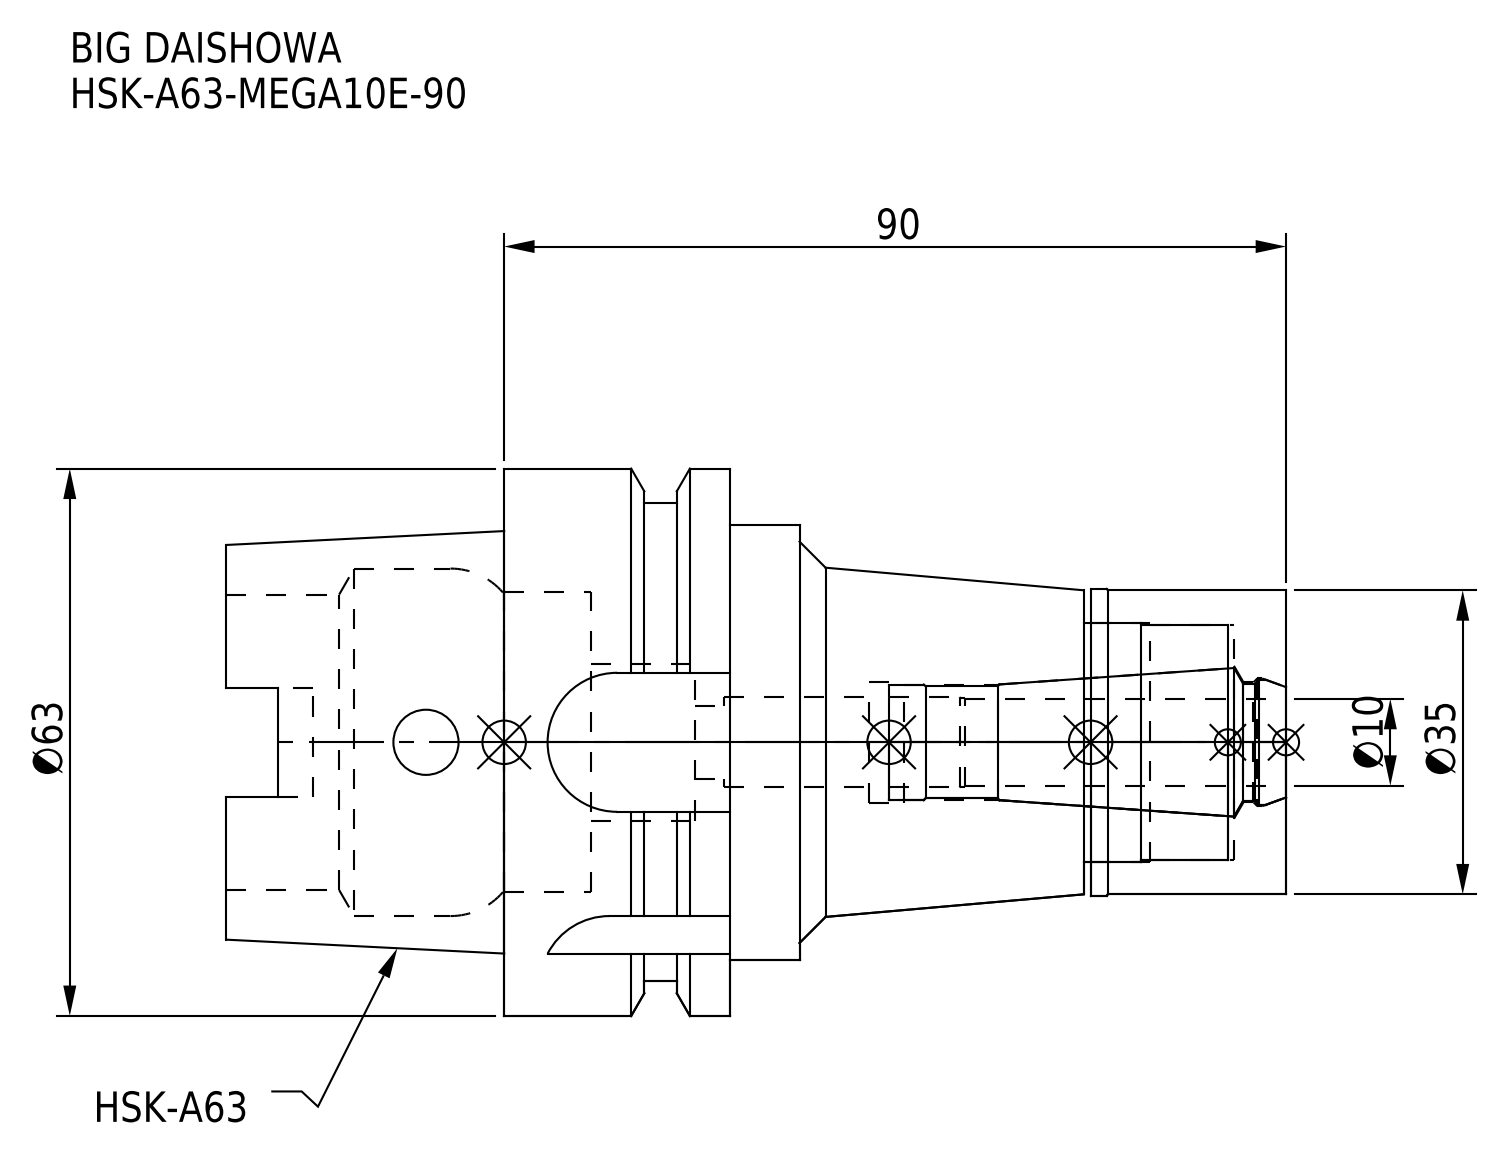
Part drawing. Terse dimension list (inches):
name: HSK-A63-MEGA10E-90_1.stp; HSK-A63-MEGA10E-90-100.stp; HSK-A63-MEGA10E-90; HSK-A63-MEGA10E-90-100-FreeParts (+3 more)
written by: SolidWorks 2019 (CONFIG_CONTROL_DESIGN)
unit: in
bodies: 2 solids, 127 faces (45 planar, 54 cylindrical, 28 other)
size: 4.803 × 2.48 × 2.48
volume: 8.988 in³; area: 56.62 in²
holes: 1× ⌀0.295, 1× ⌀0.331, 1× ⌀0.409, 1× ⌀0.524, 1× ⌀0.543, 1× ⌀0.547, 1× ⌀0.579, 1× ⌀0.709, 1× ⌀1.063, 1× ⌀1.083, 1× ⌀1.339, 1× ⌀1.358
bosses: 1× ⌀2.48, 1× ⌀2.165, 1× ⌀1.969, 1× ⌀1.39, 1× ⌀1.378
rounds: 2× R0.11, 2× R0.113, 2× R0.315, 1× R0.354
face distances: 1.024, 2.52, 3.543, 2.283, 3.152, 0.632, 0.392, 4.803, 1.652, 1.26
